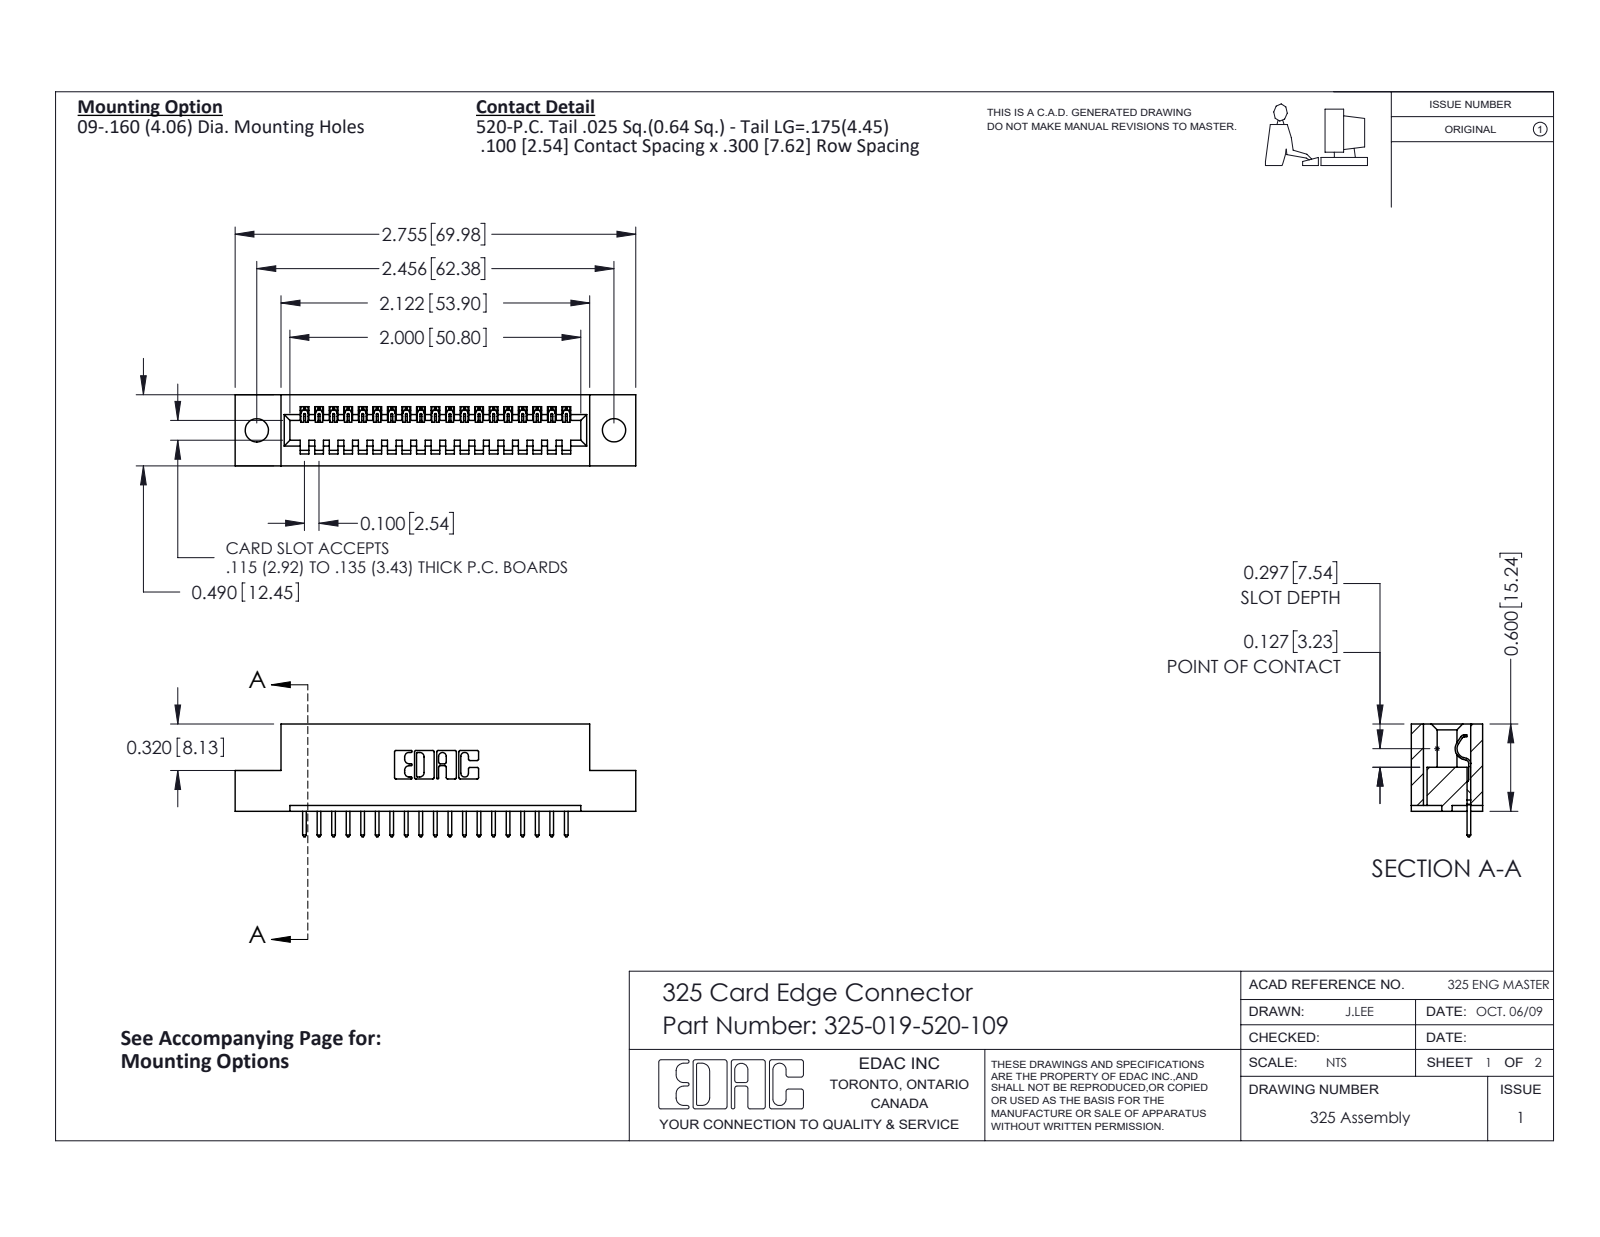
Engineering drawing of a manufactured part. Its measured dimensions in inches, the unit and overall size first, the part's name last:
Units: inches
Overall size (bounding box): 2.755 × 0.775 × 0.49
Round holes (diameter × count): ⌀0.16 ×2
Partial cylindrical surfaces — rounded edges, fillets, slot ends (radius × count): R0.006 ×38, R0.01 ×38, R0.01 ×22, R0.007 ×6, R0.031 ×6, R0.026 ×3, R0.014 ×1, R0.022 ×1
Main face-to-face distances: 0.083, 0.407, 0.3, 0.49, 0.107, 0.383, 0.025, 0.04, 0.1, 0.6
Hole centre spacings: 2.456
Volume: 0.514 in³ · Surface area: 13.19 in²
Bodies: 20 solids, 1216 faces (868 planar, 348 cylindrical, 0 other)
Part name (STEP PRODUCT): 325-292-001_325-293-120; 325 Part_.160 TH; 325-019-520-109
STEP written by: SolidWorks 2016 (CONFIG_CONTROL_DESIGN)
